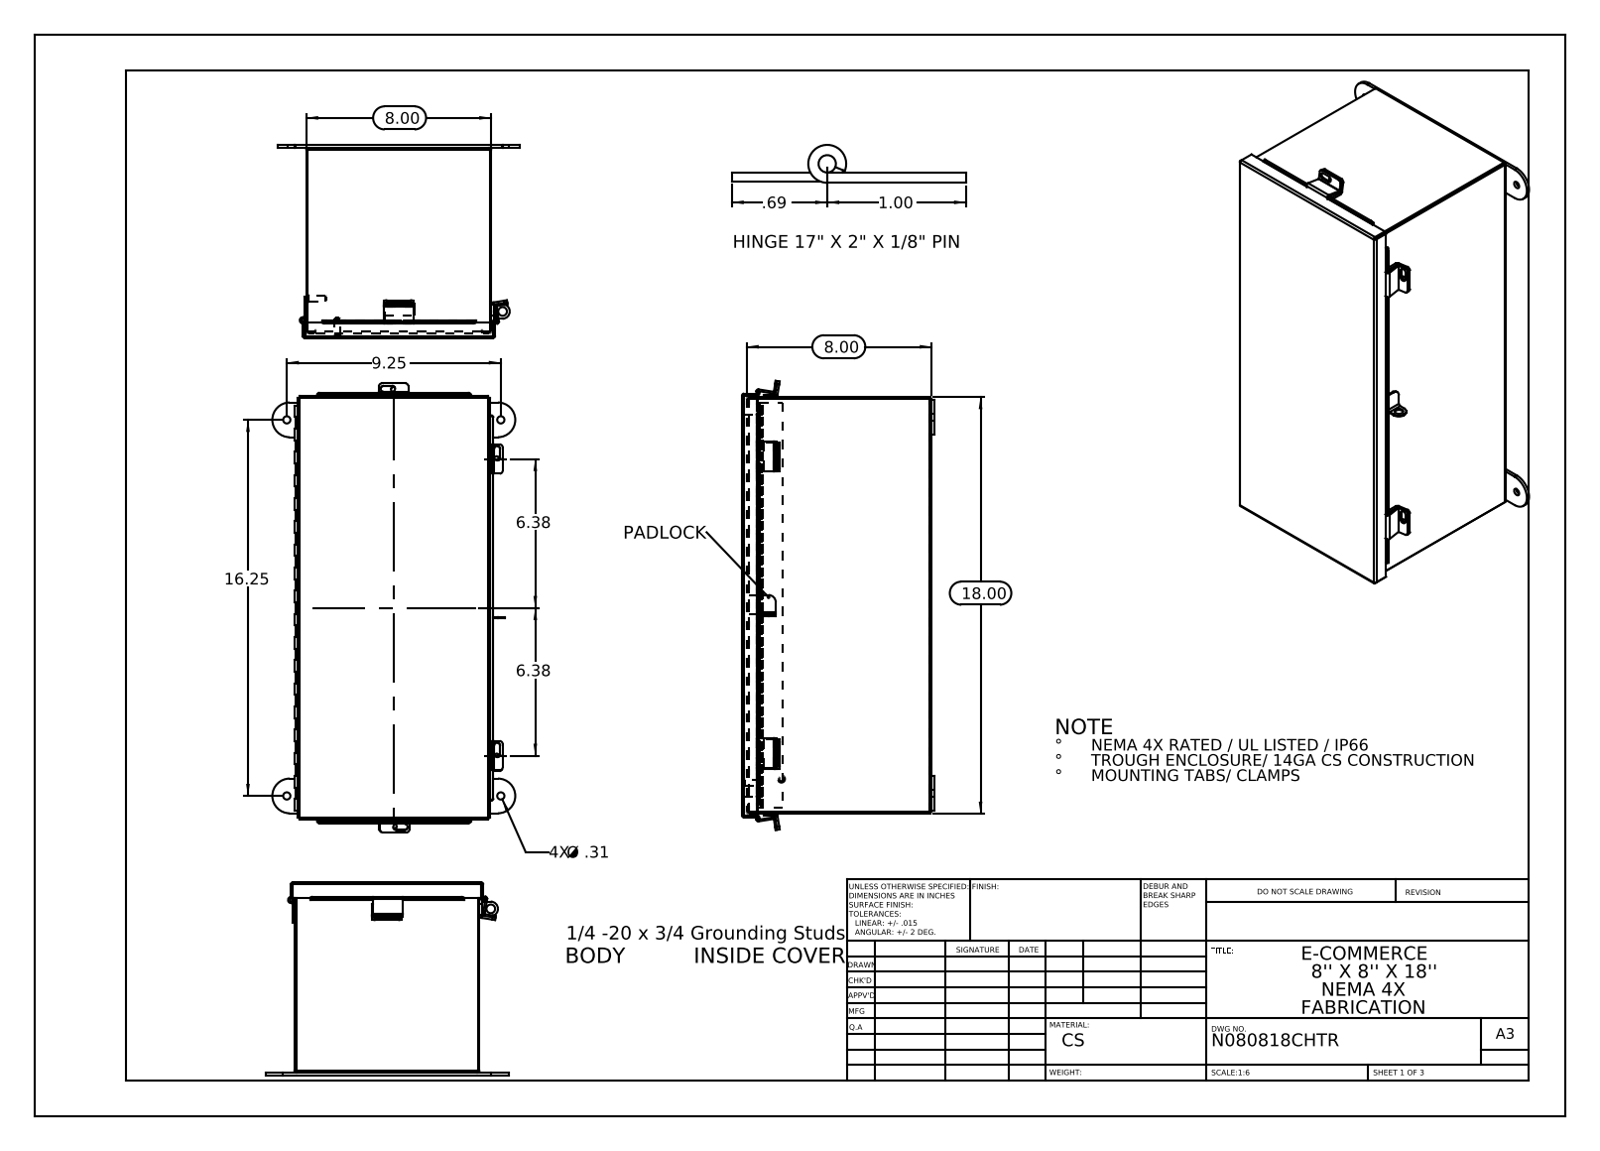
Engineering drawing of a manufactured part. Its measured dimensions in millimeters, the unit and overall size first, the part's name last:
Units: millimetres
Overall size (bounding box): 492.9 × 266.7 × 211.8
Round holes (diameter × count): ⌀6.4 ×8, ⌀4.7 ×4, ⌀8 ×4, ⌀3.2 ×1, ⌀3.2 ×1
Round bosses / shafts (diameter × count): ⌀8 ×4, ⌀8 ×2, ⌀6 ×2, ⌀6.9 ×1, ⌀6.4 ×1
Partial cylindrical surfaces — rounded edges, fillets, slot ends (radius × count): R3.2 ×15, R0.2 ×12, R0.3 ×10, R2.2 ×10, R3.4 ×8, R2.1 ×6, R2.5 ×6, R19.1 ×4
Main face-to-face distances: 1.9, 201.3, 206.5, 199.4, 203.2, 208.4, 204.5, 455.3, 12.7, 14.6
Hole centre spacings: 412.8, 456.6, 36.6, 36.6, 161.9, 198.5, 198.5, 235
Volume: 1 187 000 mm³ · Surface area: 1 245 000 mm²
Bodies: 23 solids, 754 faces (458 planar, 276 cylindrical, 20 other)
Part name (STEP PRODUCT): N080818SSCHTR JIC_Cover_Template; N080818SSCHTR HW-CD-S-25020-034; N080818SSCHTR _JIC Hinge; N080818SSCHTR JIC Mounting Bracket (+8 more)
STEP written by: SolidWorks 2013 (CONFIG_CONTROL_DESIGN)
